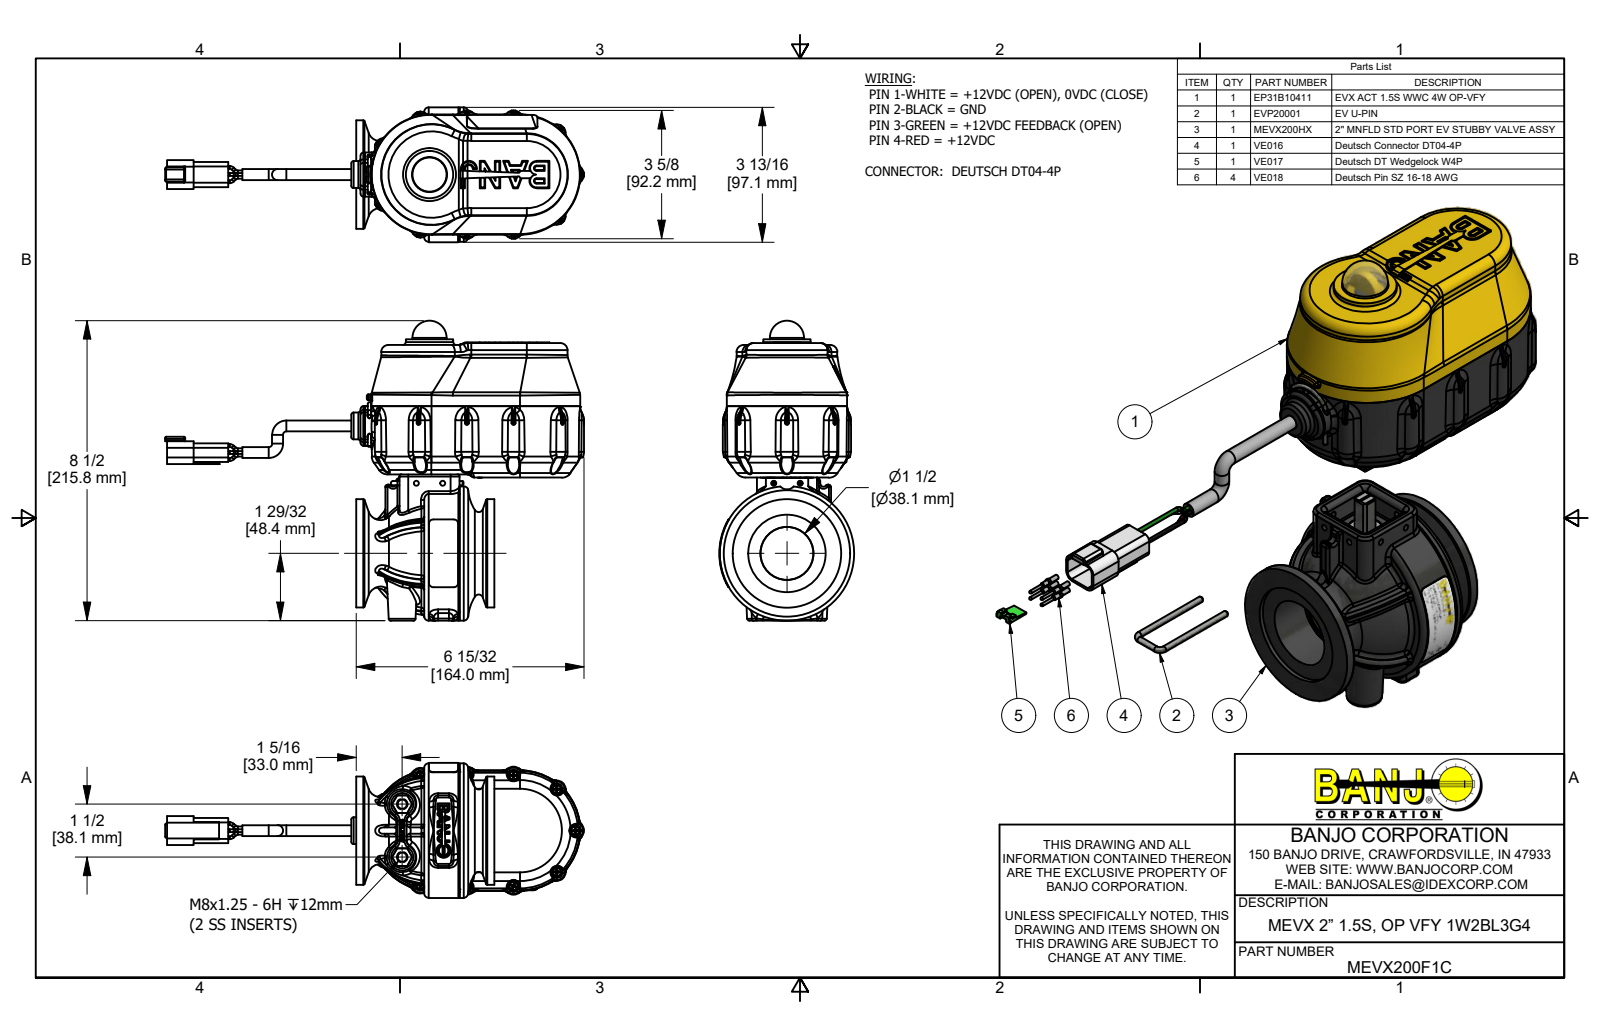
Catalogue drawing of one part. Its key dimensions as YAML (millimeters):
part_name: "MEVX200F1C; EP31B10411; B61905PPHS; B632038PM (+8 more)"
step_written_by: "Autodesk Inventor 2019 (AUTOMOTIVE_DESIGN)"
units: millimeters
bodies: {solids: 90, faces: 11145, planar: 3084, cylindrical: 3172, other: 4889}
overall_size: [301.5, 215.8, 97.1]
volume: 865200
surface_area: 379500
round_holes:
  - {diameter: 2.4, count: 11}
  - {diameter: 3.8, count: 11}
  - {diameter: 3.8, count: 8}
  - {diameter: 2, count: 7}
  - {diameter: 3.4, count: 5}
  - {diameter: 0.8, count: 4}
  - {diameter: 1.5, count: 4}
  - {diameter: 2.7, count: 4}
  - {diameter: 3.2, count: 4}
  - {diameter: 3.5, count: 4}
  - {diameter: 3.8, count: 4}
  - {diameter: 4.3, count: 4}
round_bosses_or_shafts:
  - {diameter: 2, count: 20}
  - {diameter: 6.4, count: 17}
  - {diameter: 3.6, count: 11}
  - {diameter: 2.7, count: 11}
  - {diameter: 2.2, count: 11}
  - {diameter: 1.5, count: 8}
  - {diameter: 6.9, count: 4}
  - {diameter: 5.6, count: 4}
partial_cylinders:
  - {radius: 0.3, count: 180}
  - {radius: 1, count: 145}
  - {radius: 0.3, count: 84}
  - {radius: 0.5, count: 70}
  - {radius: 0.1, count: 53}
  - {radius: 1.5, count: 45}
  - {radius: 0.8, count: 38}
  - {radius: 3.2, count: 34}
face_to_face_distances: [2.5, 1.5, 65.2, 18.5, 63.8, 5.4, 3.8, 48.2, 46.6, 42.8]
hole_center_spacings: [67.5, 4.2, 38.4, 42.2, 51.4, 72.4, 74, 96.2]
